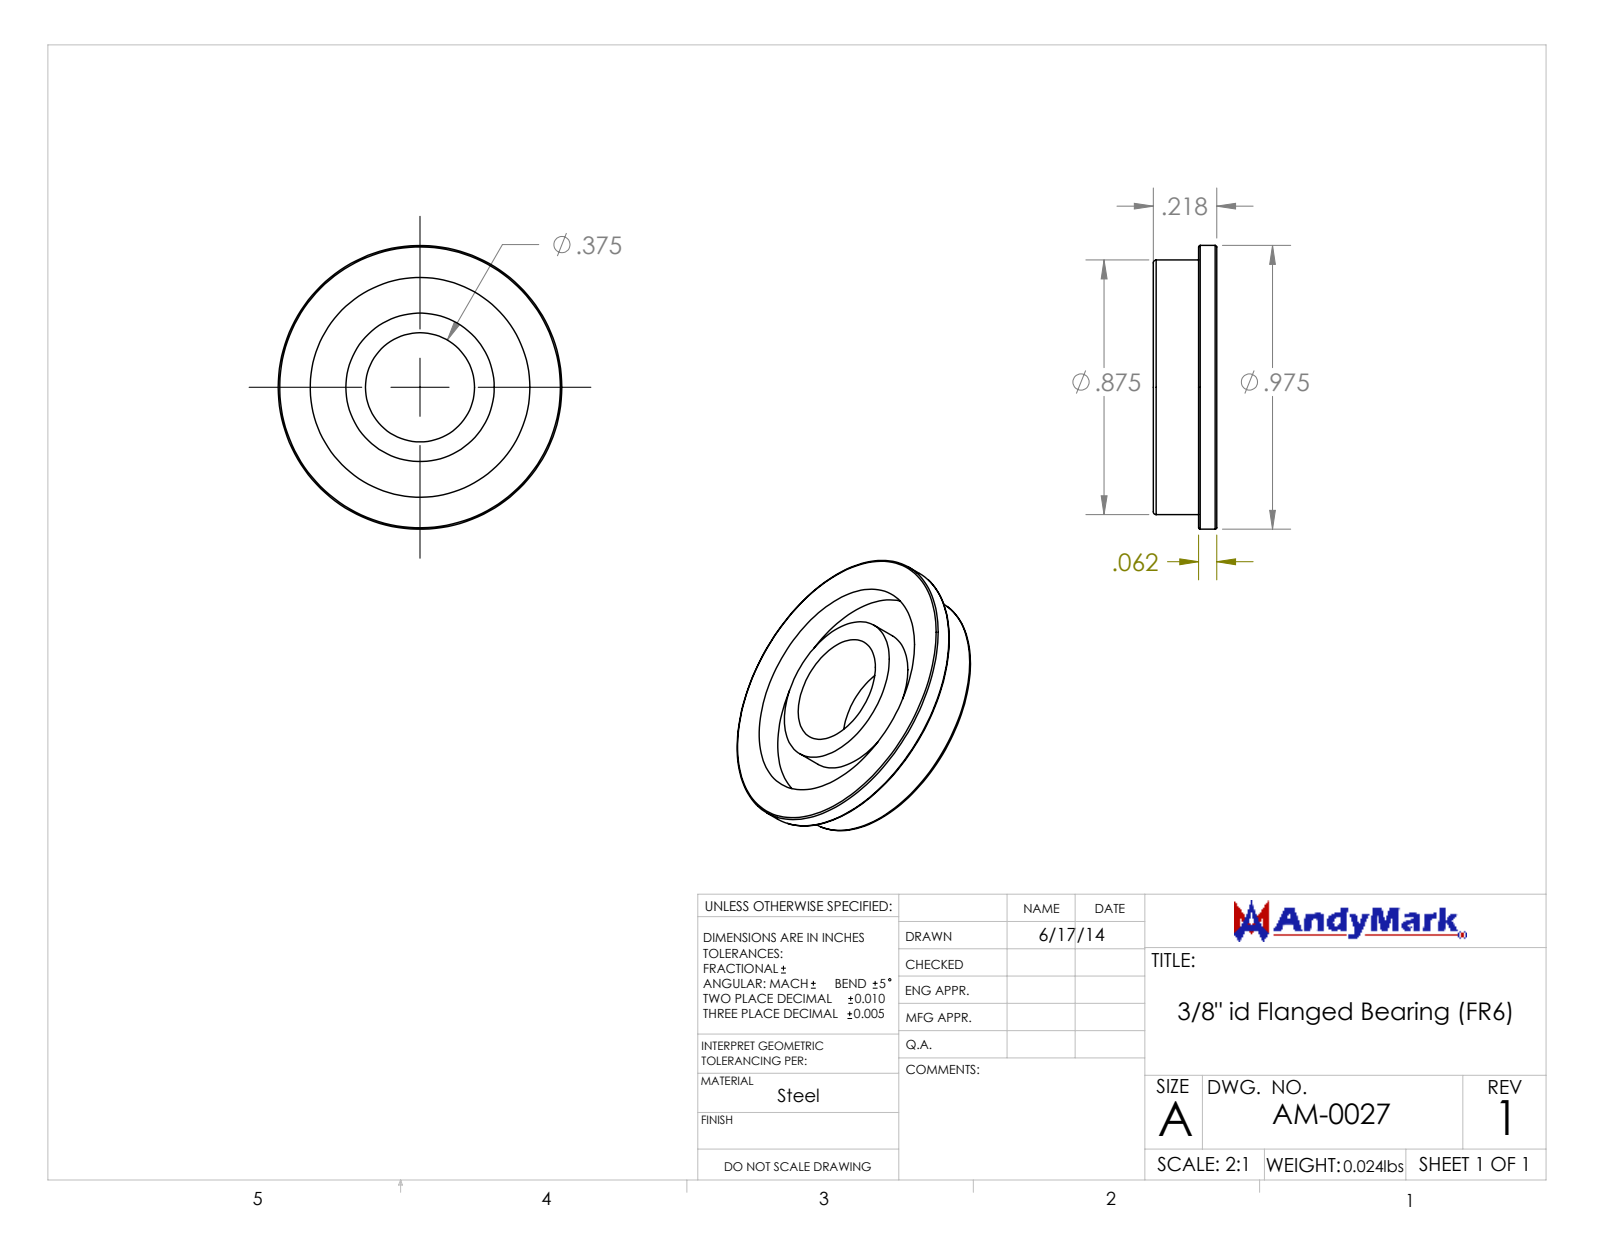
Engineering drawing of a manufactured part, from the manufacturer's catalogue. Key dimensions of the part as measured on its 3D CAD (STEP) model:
Part name (STEP PRODUCT): am-0027 0.375'''''''' id Flanged Bearing (FR6)
STEP written by: SolidWorks 2014 (AUTOMOTIVE_DESIGN)
Units: inches
Bodies: 1 solid, 27 faces (7 planar, 14 cylindrical, 6 other)
Overall size (bounding box): 0.975 × 0.975 × 0.218
Volume: 0.072 in³ · Surface area: 2.838 in²
Round holes (diameter × count): ⌀0.375 ×1, ⌀0.755 ×1
Round bosses / shafts (diameter × count): ⌀0.975 ×1, ⌀0.875 ×1, ⌀0.51 ×1
Main face-to-face distances: 0.09, 0.128, 0.038, 0.218, 0.156, 0.066, 0.028, 0.062
